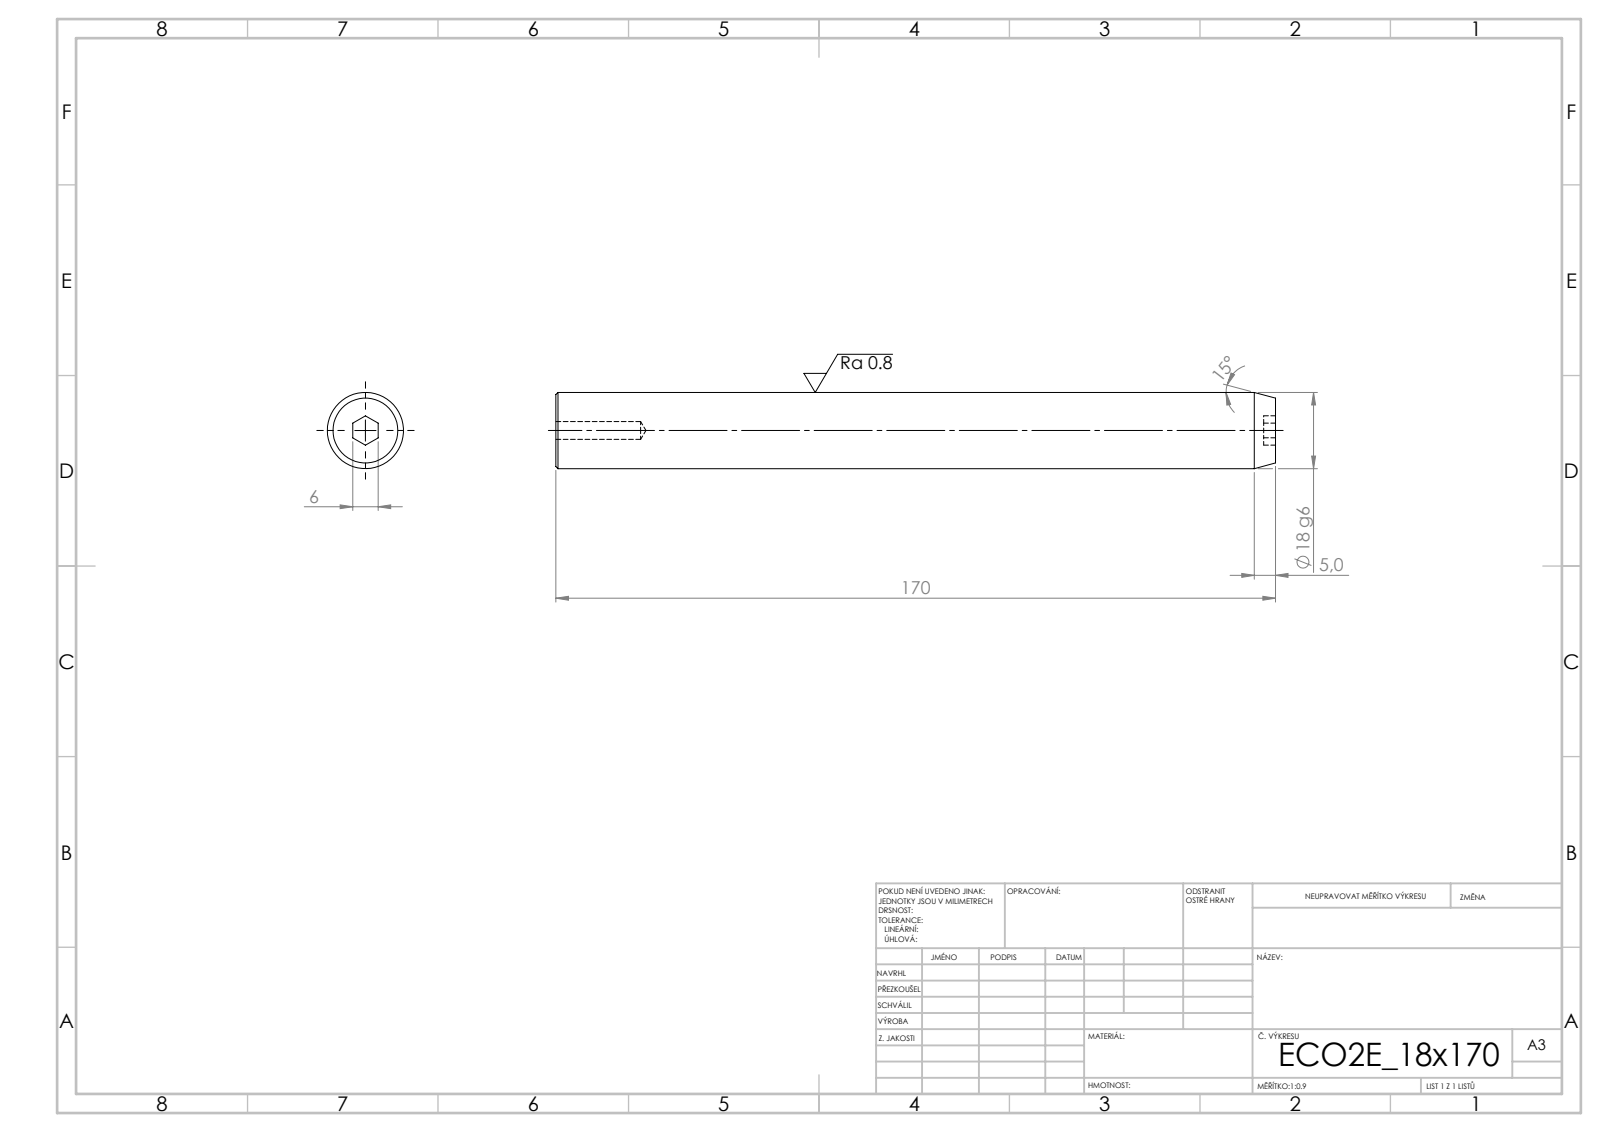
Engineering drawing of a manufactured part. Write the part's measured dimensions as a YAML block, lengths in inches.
step_written_by: "SolidWorks 2019 (CONFIG_CONTROL_DESIGN)"
units: inches
bodies: {solids: 1, faces: 19, planar: 9, cylindrical: 4, other: 6}
overall_size: [6.693, 0.709, 0.709]
volume: 2.606
surface_area: 16.04
round_holes:
  - {diameter: 0.165, count: 1}
round_bosses_or_shafts:
  - {diameter: 0.709, count: 1}
face_to_face_distances: [6.693, 0.11, 6.583, 0.236]
